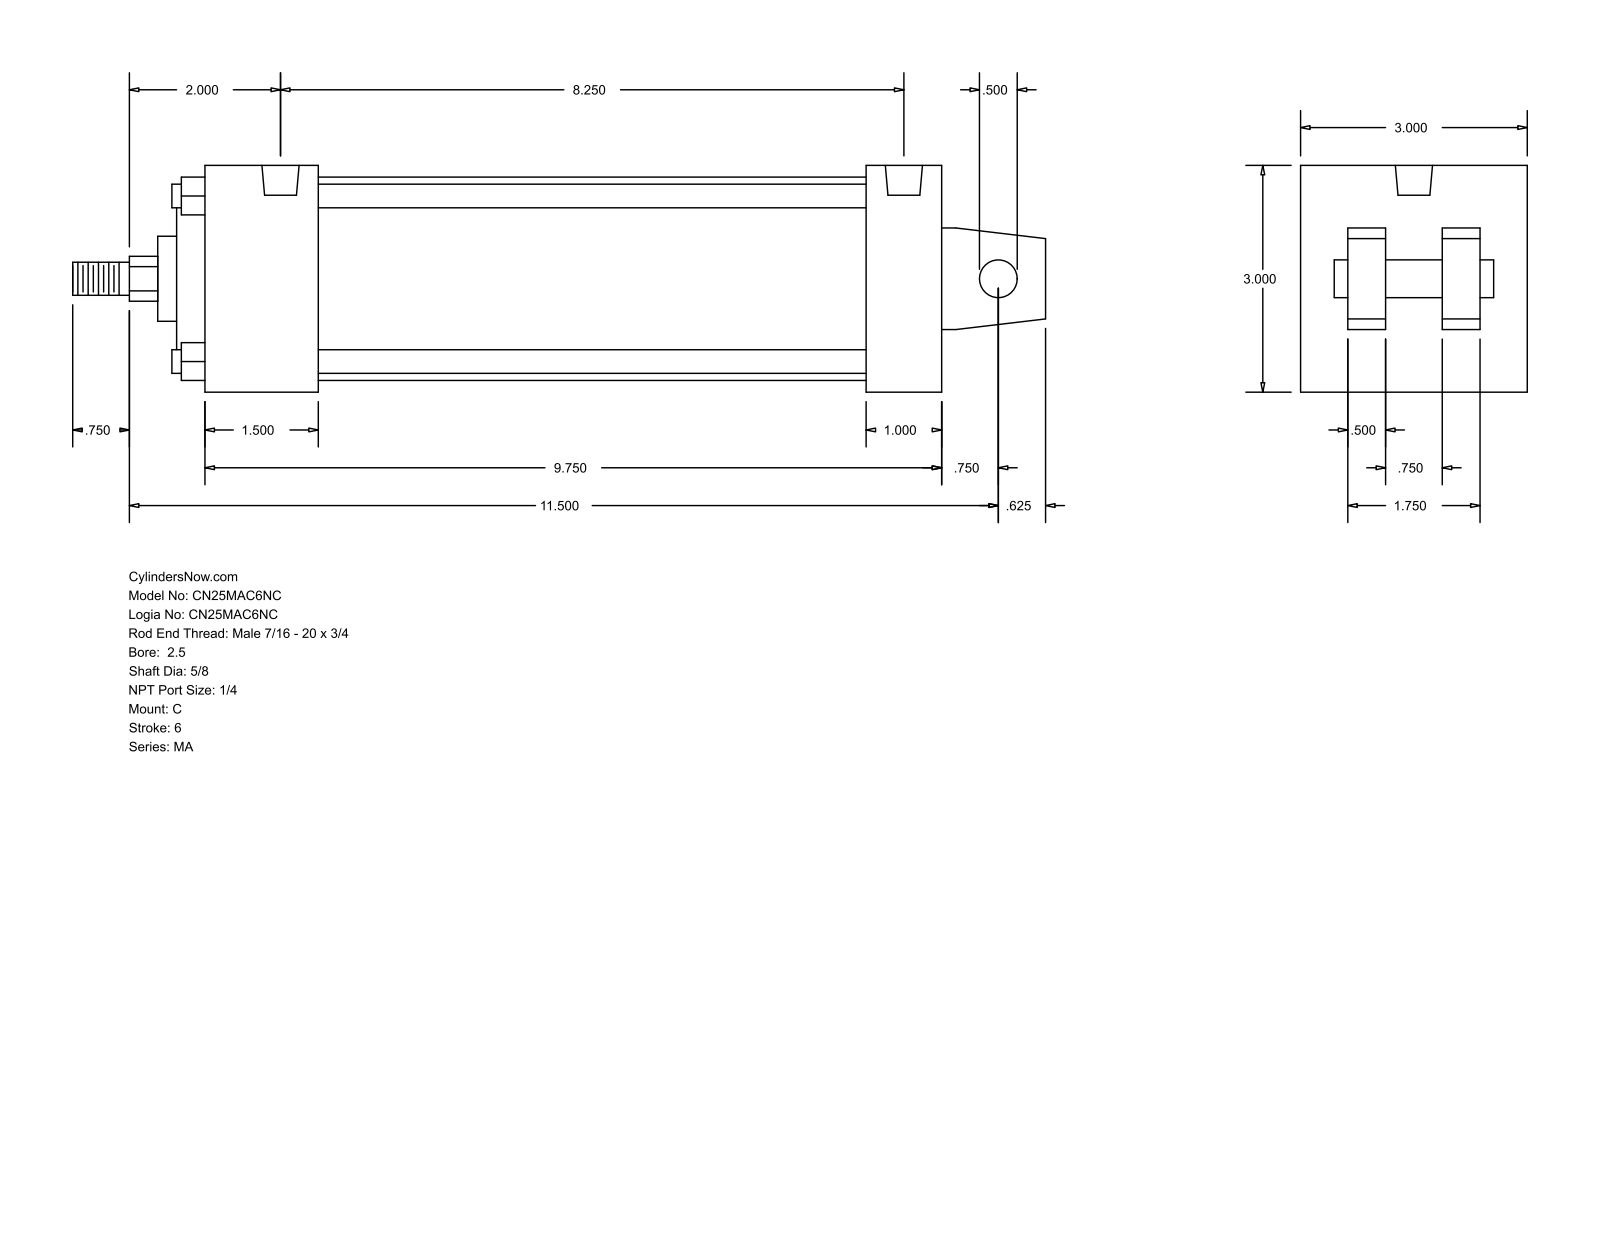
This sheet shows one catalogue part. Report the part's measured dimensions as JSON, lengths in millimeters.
{"part_name": "MA_C__0250_0.625", "step_written_by": "GSSL Pune (CONFIG_CONTROL_DESIGN)", "units": "millimeters", "bodies": {"solids": 0, "faces": 105, "planar": 77, "cylindrical": 28, "other": 0}, "overall_size": [327.02, 76.2, 76.2], "round_holes": [[7.94, 4], [12.49, 2]], "round_bosses_or_shafts": [[7.94, 4], [68.33, 1], [50.8, 1], [28.57, 1], [15.88, 1], [12.7, 1], [11.11, 1]], "partial_cylinders_radius": [[7.54, 1]], "face_to_face_distances": [76.2, 247.65, 12.7, 15.87, 60.33, 47.63, 25.4, 38.1, 222.25, 184.15], "hole_center_spacings": [209.55]}
